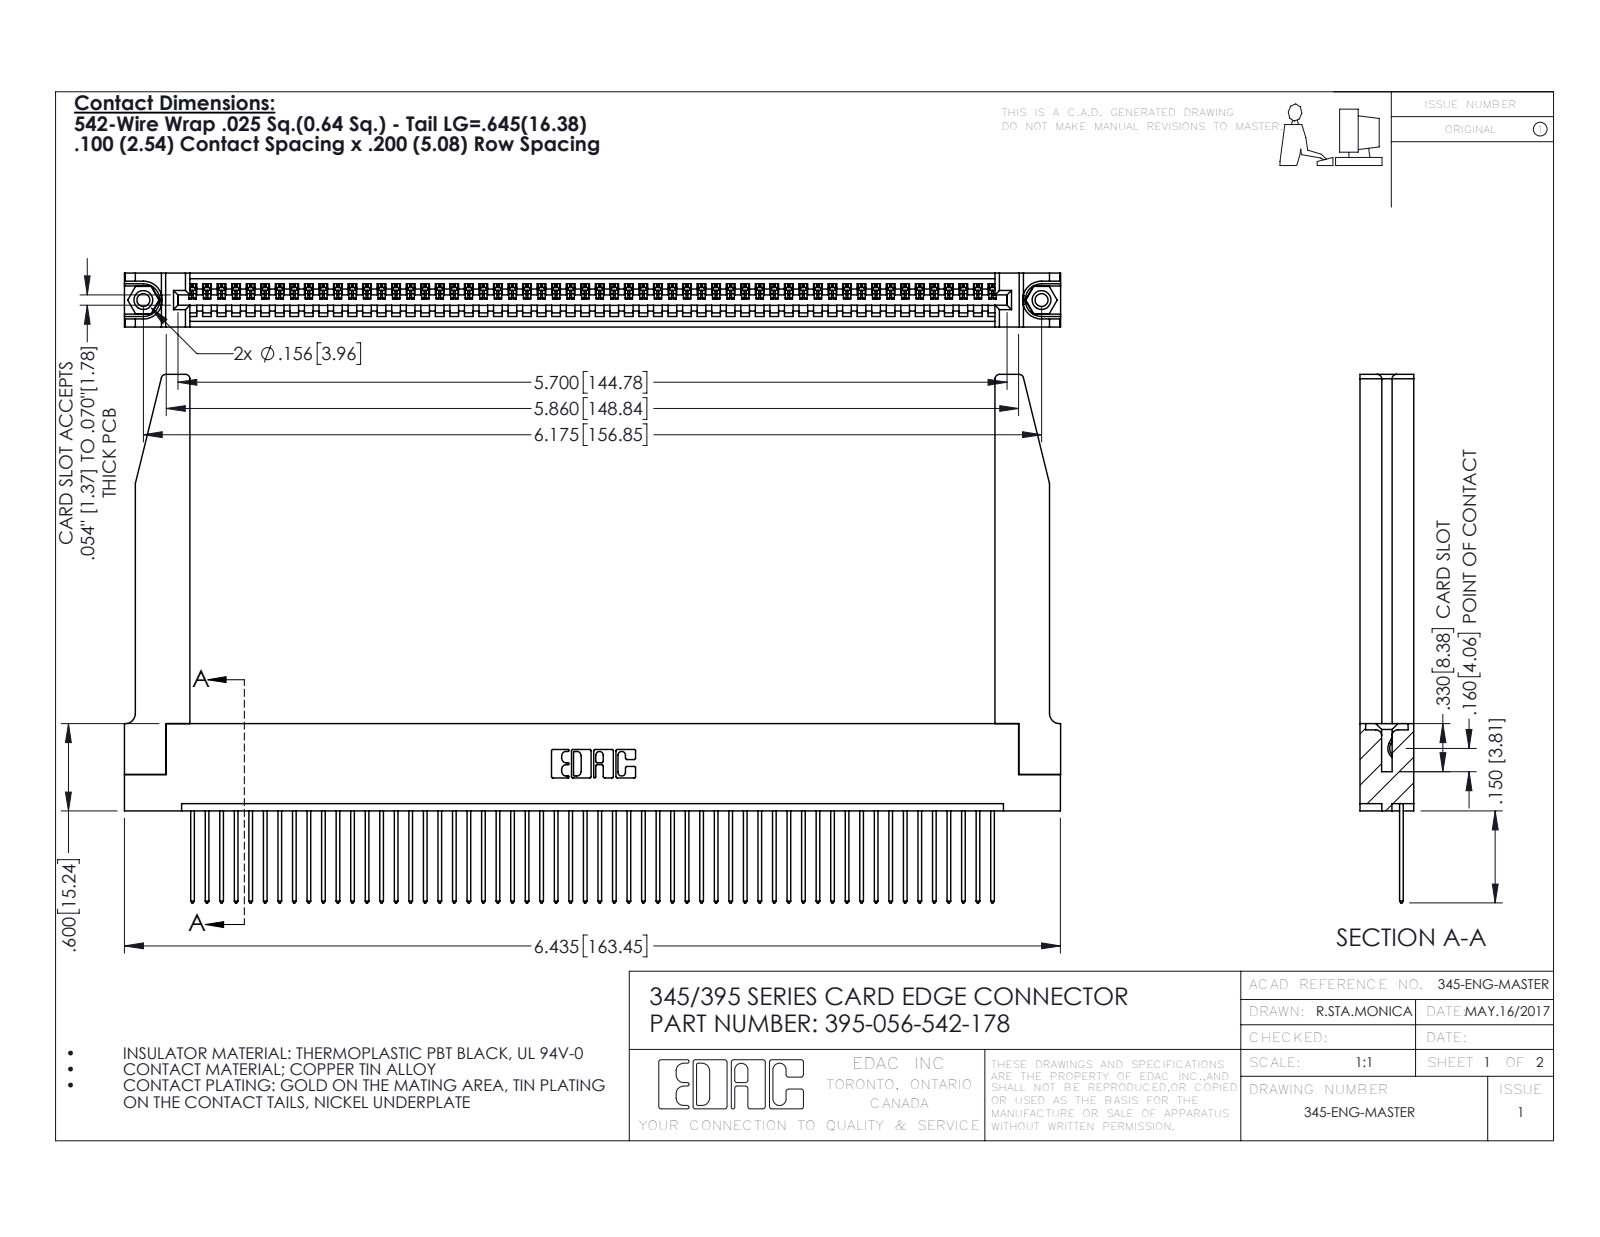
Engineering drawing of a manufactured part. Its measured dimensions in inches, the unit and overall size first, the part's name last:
Units: inches
Overall size (bounding box): 6.436 × 3.632 × 0.37
Round holes (diameter × count): ⌀0.089 ×2, ⌀0.125 ×2, ⌀0.156 ×2, ⌀0.064 ×1
Round bosses / shafts (diameter × count): ⌀0.155 ×2
Partial cylindrical surfaces — rounded edges, fillets, slot ends (radius × count): R0.006 ×112, R0.01 ×112, R0.01 ×22, R0.03 ×8, R0.007 ×6, R0.031 ×6, R0.026 ×3, R0.031 ×2
Main face-to-face distances: 0.072, 0.298, 0.37, 0.098, 0.272, 0.025, 0.2, 0.225, 0.148, 0.15
Hole centre spacings: 0.27, 5.939, 6.175
Volume: 1.436 in³ · Surface area: 44.6 in²
Bodies: 61 solids, 3608 faces (2462 planar, 1094 cylindrical, 52 other)
Part name (STEP PRODUCT): 345-220-078_345-220-078; 345-250-001_345-250-001-102; 395-056-542-178; 345-292-001_345-293-142 (+1 more)
STEP written by: SolidWorks 2016 (CONFIG_CONTROL_DESIGN)
